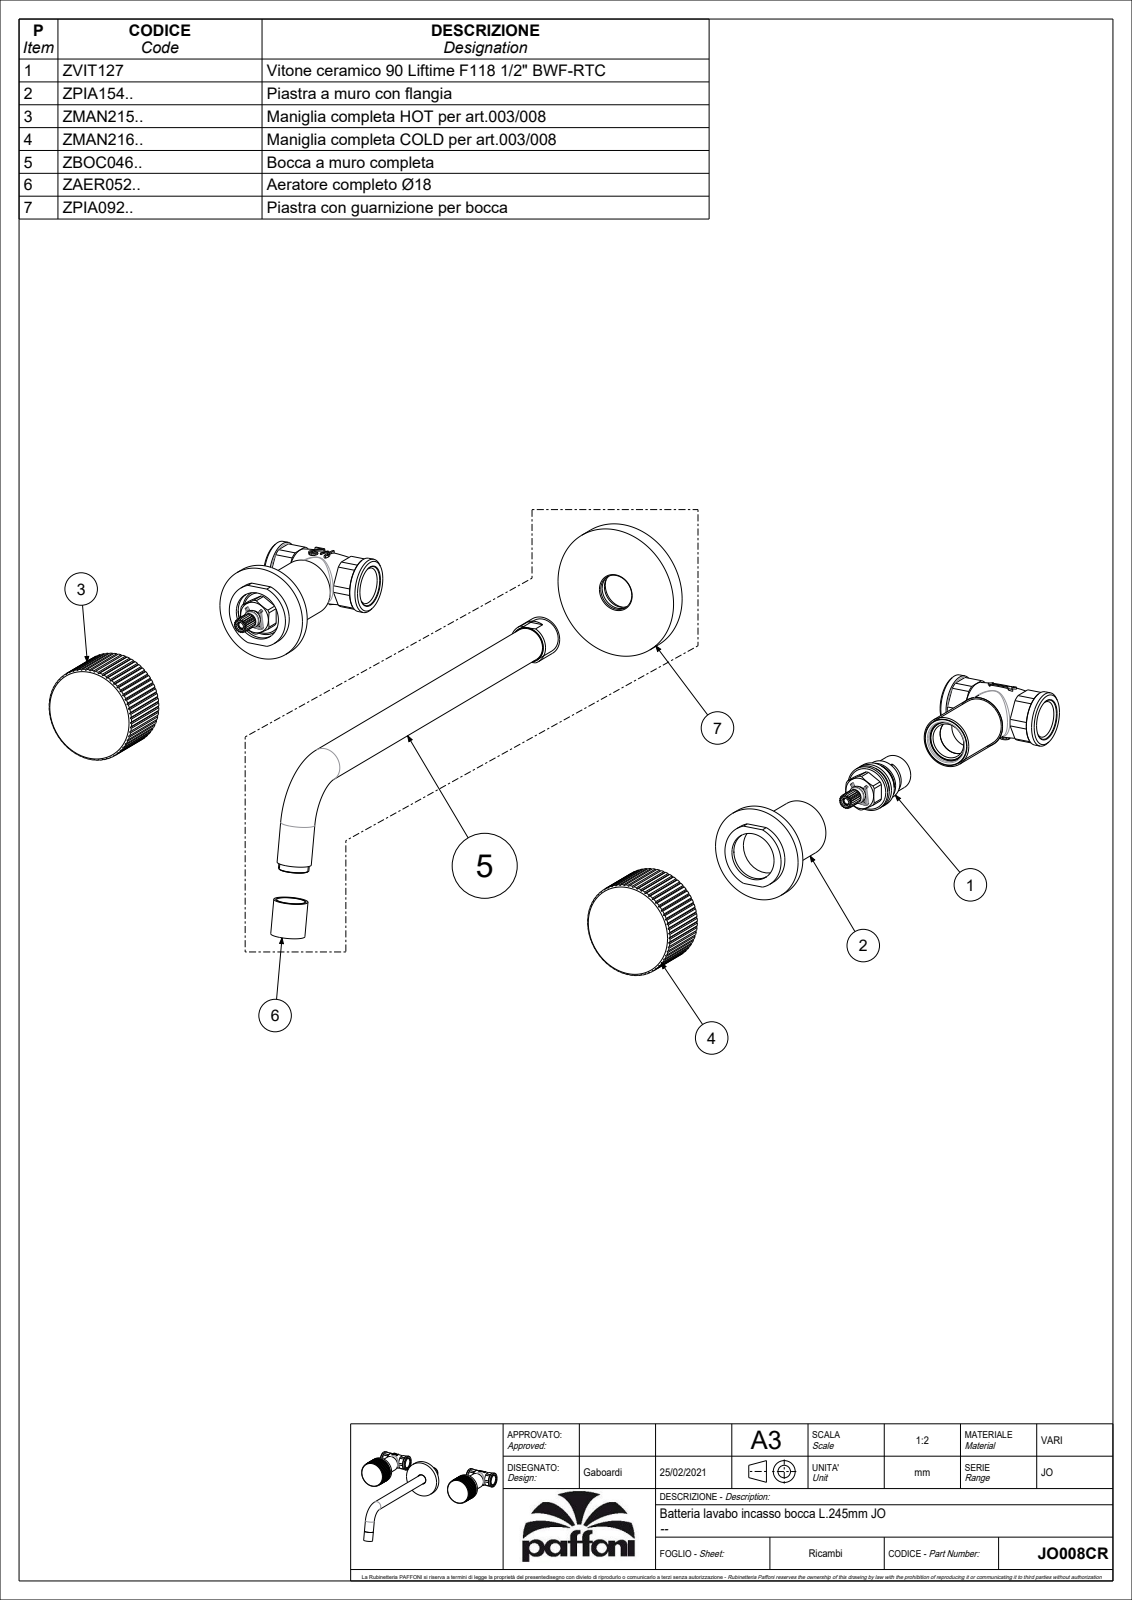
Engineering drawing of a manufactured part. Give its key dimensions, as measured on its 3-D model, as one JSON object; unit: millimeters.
{"part_name": "JO008CR", "step_written_by": "CREO PARAMETRIC BY PTC INC, 2020044 (CONFIG_CONTROL_DESIGN)", "units": "millimeters", "bodies": {"solids": 6, "faces": 1444, "planar": 636, "cylindrical": 584, "other": 224}, "overall_size": [250, 233.58, 99.78], "volume_mm3": 119597, "surface_area_mm2": 100470, "round_holes": [[0.5, 51], [15, 5], [3, 2], [4.2, 2], [5.5, 2], [8, 2], [25.5, 2], [36, 2], [41, 2], [46.2, 2], [47, 2], [11, 1]], "round_bosses_or_shafts": [[50, 2], [44, 2], [41.2, 2], [30, 2], [24, 2], [22, 2], [21.4, 2], [18, 2]], "partial_cylinders_radius": [[0.2, 52], [0.5, 24], [1, 4], [9.4, 2], [13.4, 2], [4.25, 1]], "face_to_face_distances": [2, 9, 7, 5, 4, 22.3, 20.3, 33.7, 28.7, 26.7], "hole_center_spacings": [1.5, 3.36, 2.12, 3.35, 4.75, 5.41, 6.19, 4.74]}
